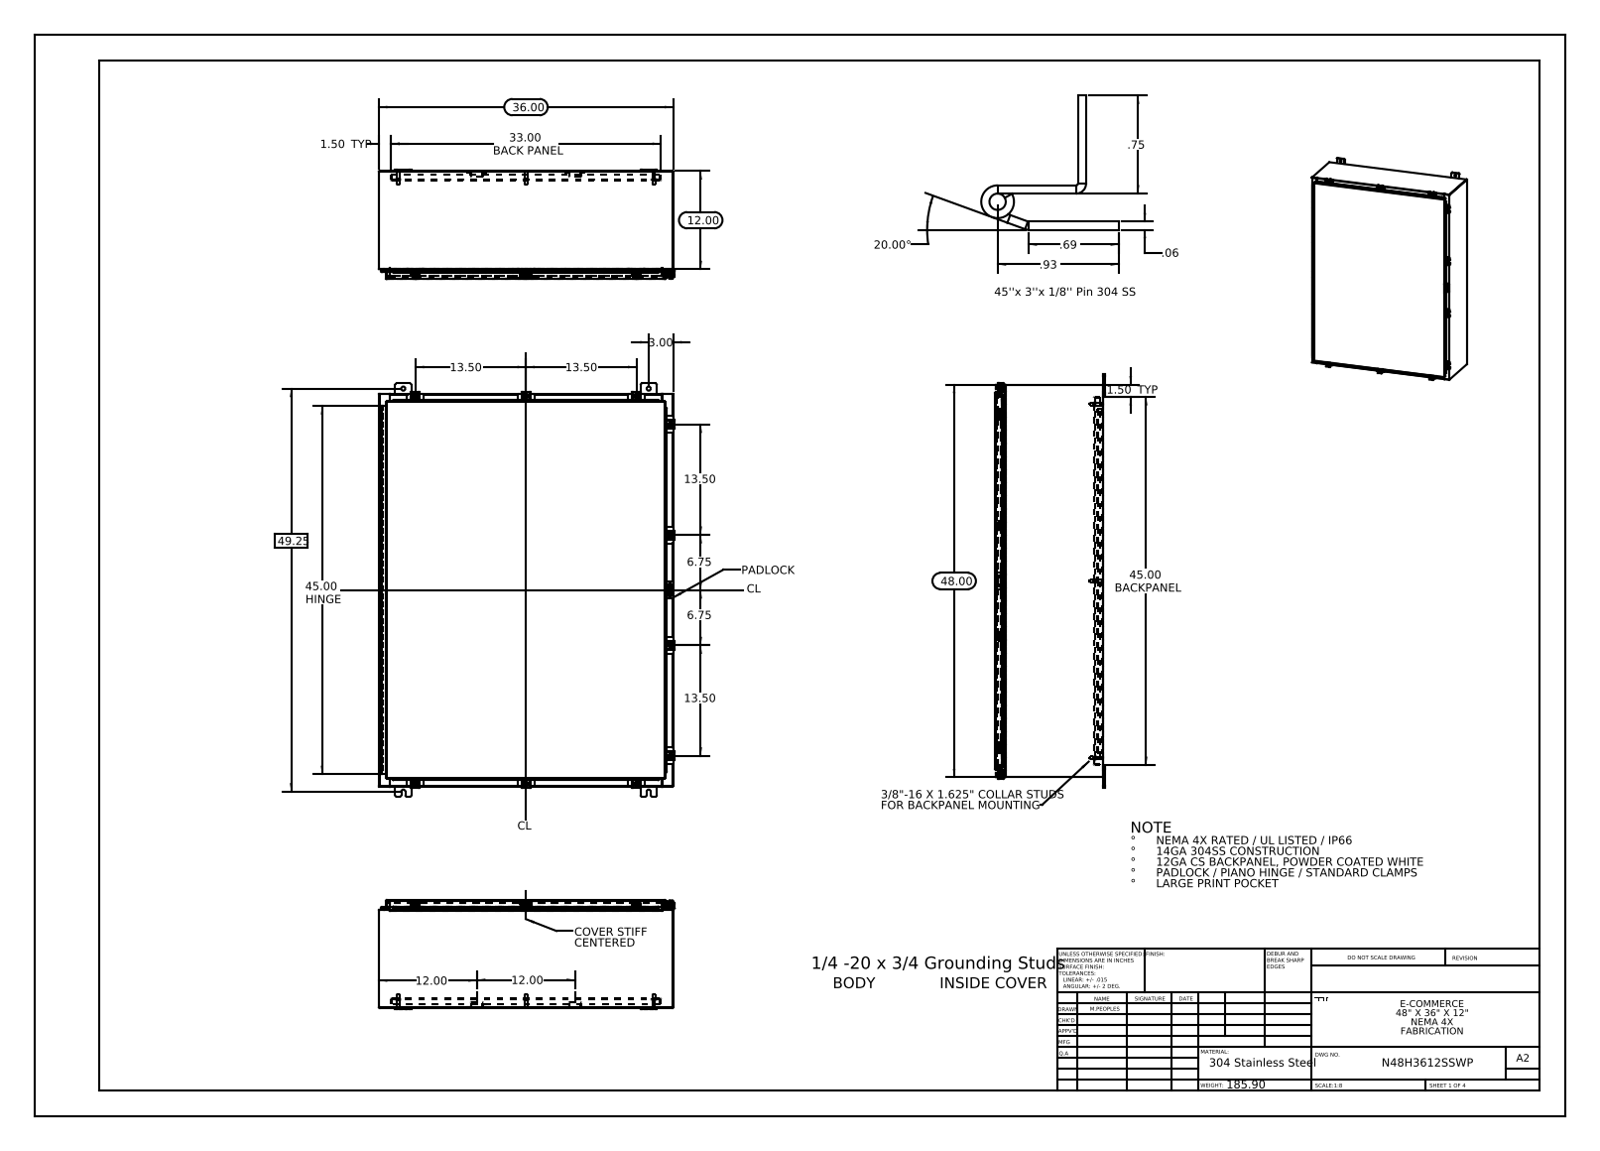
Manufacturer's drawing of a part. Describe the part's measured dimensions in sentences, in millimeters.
The part is named "N48H3612SSWP Body; N48H3612SSWP Enclosure Stiffener; N48H3612SSWP Clamp Assembly; N48H3612SSWP 22101002 (+8 more)". Its 3-D file was written by "SolidWorks 2013 (CONFIG_CONTROL_DESIGN)". It is 74 solids with 2999 faces: 1562 planar, 1269 cylindrical and 168 other. Overall it measures 1282.7 by 919.8 by 340.1 millimeters. Its volume is 10 660 000 cubic millimeters and its surface area 10 490 000 square millimeters. Round holes: 12 of diameter 12.7, 10 of diameter 5.4, 10 of diameter 6.6, 6 of diameter 6.4, 2 of diameter 3.2, 1 of diameter 3.2. Round bosses or shafts: 11 of diameter 6.4, 10 of diameter 12.7, 10 of diameter 10.1, 8 of diameter 15.9, 8 of diameter 9.5, 8 of diameter 8.4. Partial cylindrical surfaces (rounded edges, fillets, slot ends): 46 of radius 1.5, 39 of radius 0.3, 33 of radius 2.2, 24 of radius 4.8, 20 of radius 3, 20 of radius 3.6, 15 of radius 1.3, 14 of radius 2. The main face-to-face distances are 1.9, 333.4, 331.5, 2.6, 335.3, 25.4, 308, 27.3, 306.1, 29.9. The hole center spacings are 342.9, 347, 508, 511.1, 549.3, 605, 685.8, 965.3.
